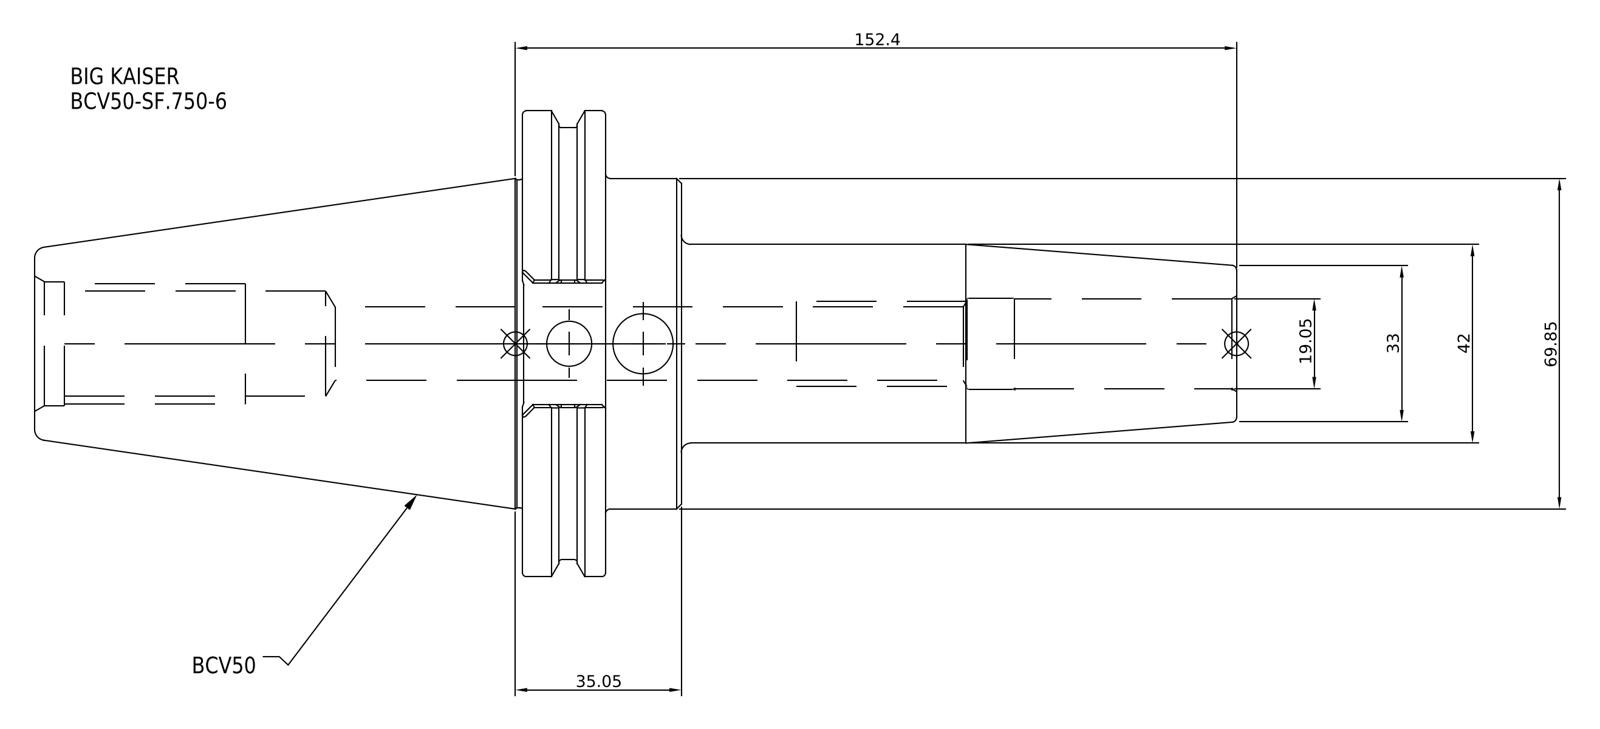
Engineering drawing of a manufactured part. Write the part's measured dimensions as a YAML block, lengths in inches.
part_name: "BCV50-SF_750-6"
step_written_by: "SolidWorks 2021 (CONFIG_CONTROL_DESIGN)"
units: inches
bodies: {solids: 1, faces: 30, planar: 8, cylindrical: 14, other: 8}
overall_size: [10, 3.875, 3.875]
volume: 35.16
surface_area: 89.84
round_holes:
  - {diameter: 0.75, count: 1}
round_bosses_or_shafts:
  - {diameter: 3.875, count: 1}
  - {diameter: 3.594, count: 1}
  - {diameter: 2.75, count: 1}
  - {diameter: 1.654, count: 1}
face_to_face_distances: [0.691, 0.63, 1.321, 5.38, 4.75, 4.059, 4.62, 5.25, 5.941, 10]
